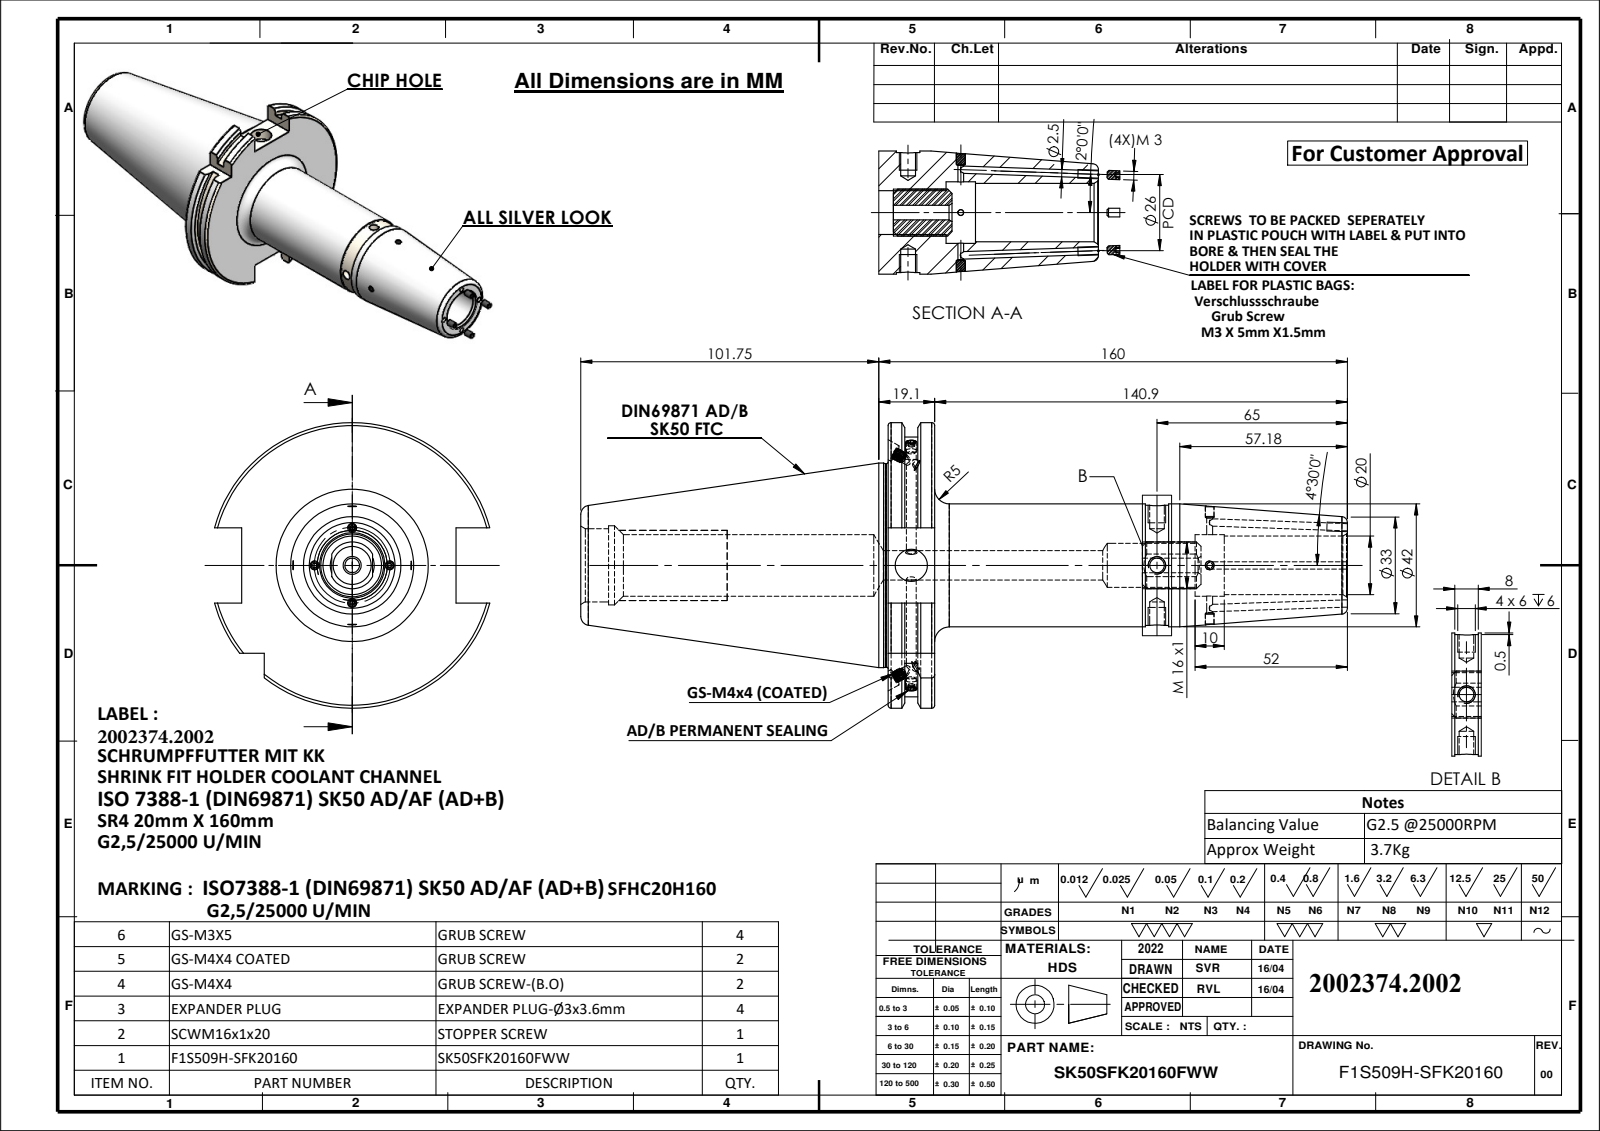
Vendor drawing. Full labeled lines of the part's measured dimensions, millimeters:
Part name (STEP PRODUCT): GS-M3X5; SK50SFK20160FWW; F1S509H-SFK20160; SCWM16X1X20-FLAT (+3 more)
STEP written by: SolidWorks 2024 (AUTOMOTIVE_DESIGN)
Units: millimetres
Bodies: 14 solids, 445 faces (133 planar, 134 cylindrical, 178 other)
Overall size (bounding box): 269.79 × 97.5 × 94.05
Volume: 477 881 mm³ · Surface area: 72 781 mm²
Round holes (diameter × count): ⌀2.5 ×4, ⌀5 ×3, ⌀2 ×2, ⌀3 ×2, ⌀3.2 ×2, ⌀6 ×2, ⌀3.3 ×1, ⌀10 ×1, ⌀11 ×1, ⌀15 ×1, ⌀20 ×1, ⌀21 ×1
Round bosses / shafts (diameter × count): ⌀4 ×4, ⌀3 ×4, ⌀2.9 ×2, ⌀69.85 ×1, ⌀69.45 ×1, ⌀42 ×1, ⌀41 ×1
Partial cylindrical surfaces — rounded edges, fillets, slot ends (radius × count): R8 ×1, R44.9 ×1, R48.75 ×1
Main face-to-face distances: 15.9, 5.66, 10.24, 10.14, 4.48, 5.76, 104.95, 110.61, 115.09, 120.85
Hole centre spacings: 18, 83.9, 101.9
